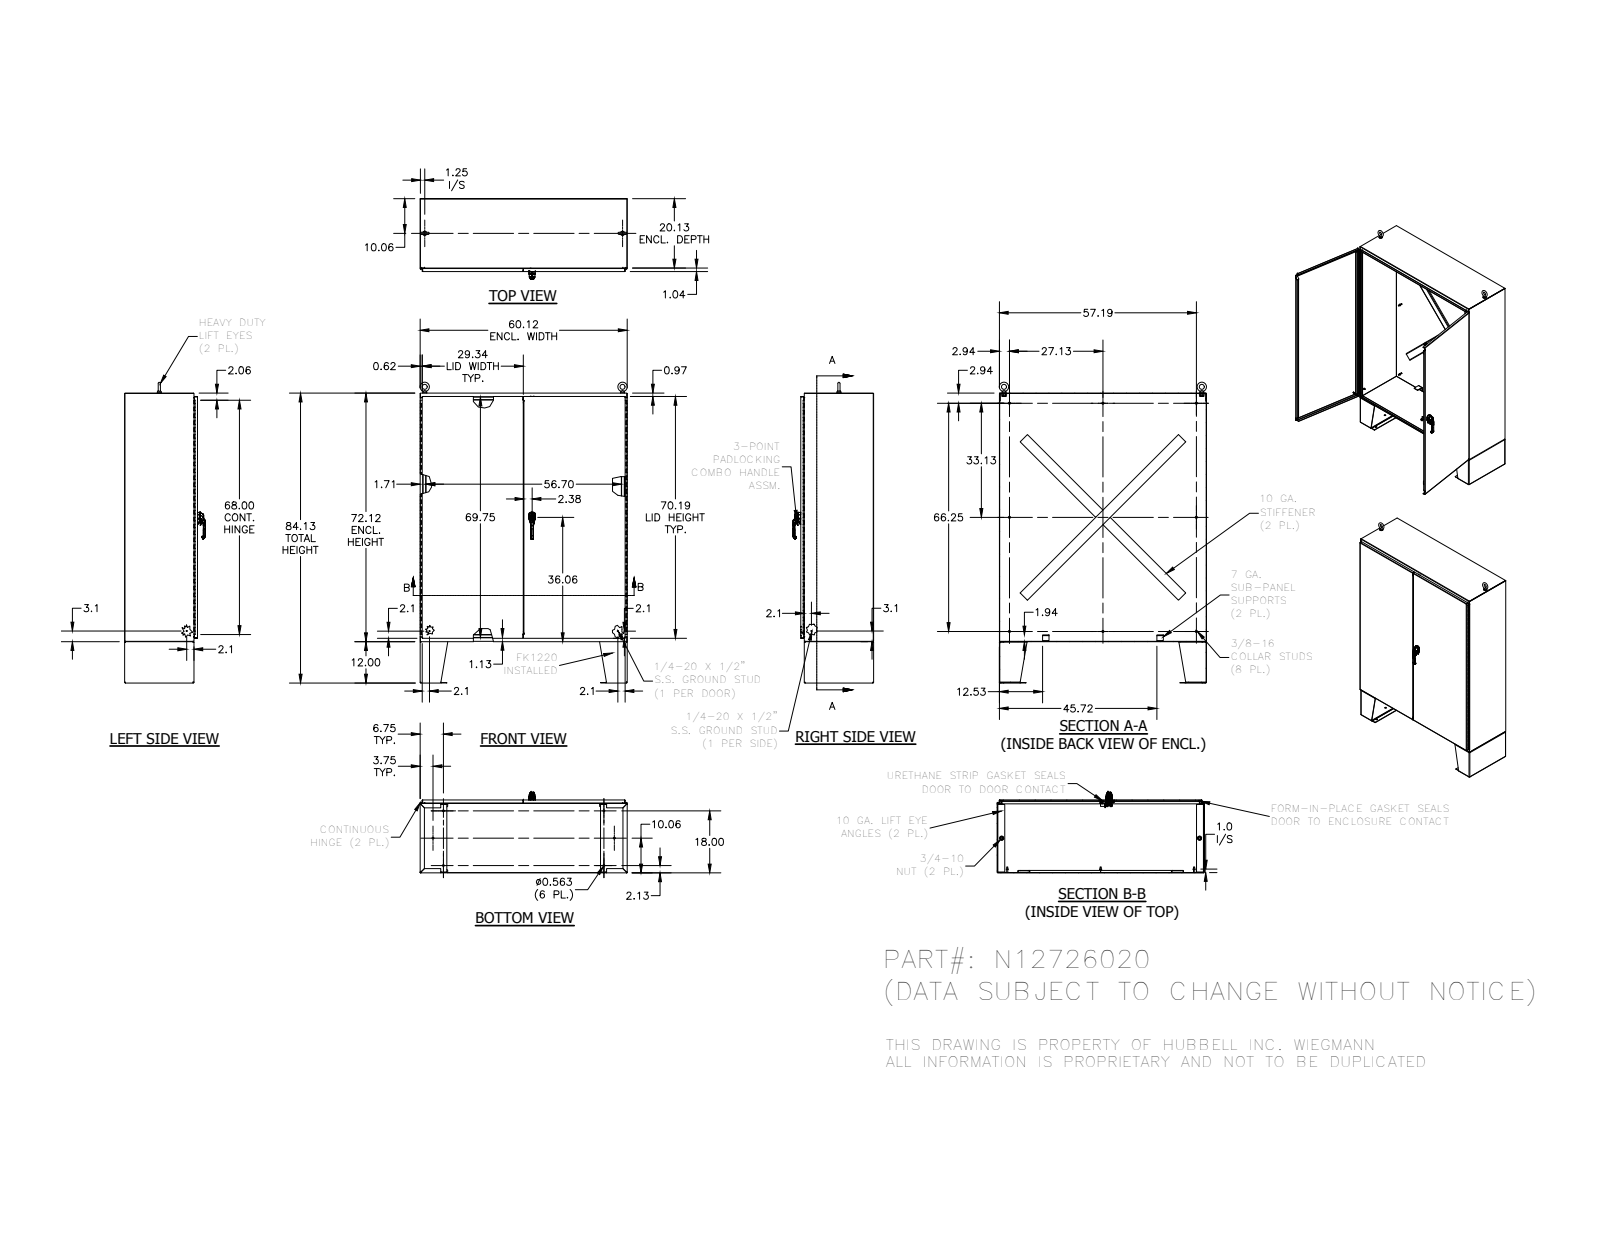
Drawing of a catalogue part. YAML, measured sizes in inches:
part_name: "N12726020"
step_written_by: "SolidWorks 2018 (AUTOMOTIVE_DESIGN)"
units: inches
bodies: {solids: 76, faces: 2596, planar: 1528, cylindrical: 768, other: 300}
overall_size: [87.248, 60.125, 23.338]
volume: 1738
surface_area: 35123
round_holes:
  - {diameter: 0.563, count: 18}
  - {diameter: 0.277, count: 8}
  - {diameter: 0.2, count: 4}
  - {diameter: 0.125, count: 3}
  - {diameter: 0.28, count: 3}
  - {diameter: 0.241, count: 2}
  - {diameter: 0.25, count: 2}
  - {diameter: 0.252, count: 2}
  - {diameter: 0.4, count: 2}
  - {diameter: 0.45, count: 2}
  - {diameter: 0.642, count: 2}
  - {diameter: 0.813, count: 2}
round_bosses_or_shafts:
  - {diameter: 0.33, count: 8}
  - {diameter: 0.625, count: 6}
  - {diameter: 0.25, count: 5}
  - {diameter: 0.337, count: 3}
  - {diameter: 1.25, count: 2}
  - {diameter: 1.12, count: 2}
  - {diameter: 1, count: 2}
  - {diameter: 0.75, count: 2}
partial_cylinders:
  - {radius: 0.031, count: 24}
  - {radius: 0.094, count: 23}
  - {radius: 0.219, count: 22}
  - {radius: 0.05, count: 18}
  - {radius: 0.025, count: 16}
  - {radius: 0.125, count: 15}
  - {radius: 0.03, count: 13}
  - {radius: 0.067, count: 8}
face_to_face_distances: [0.094, 21.067, 20.973, 21.16, 60.031, 72.031, 60.125, 59.938, 71.938, 72.125]
hole_center_spacings: [2.041, 5, 16.876, 18.75, 19.405, 46.398, 49.501, 50.256]
